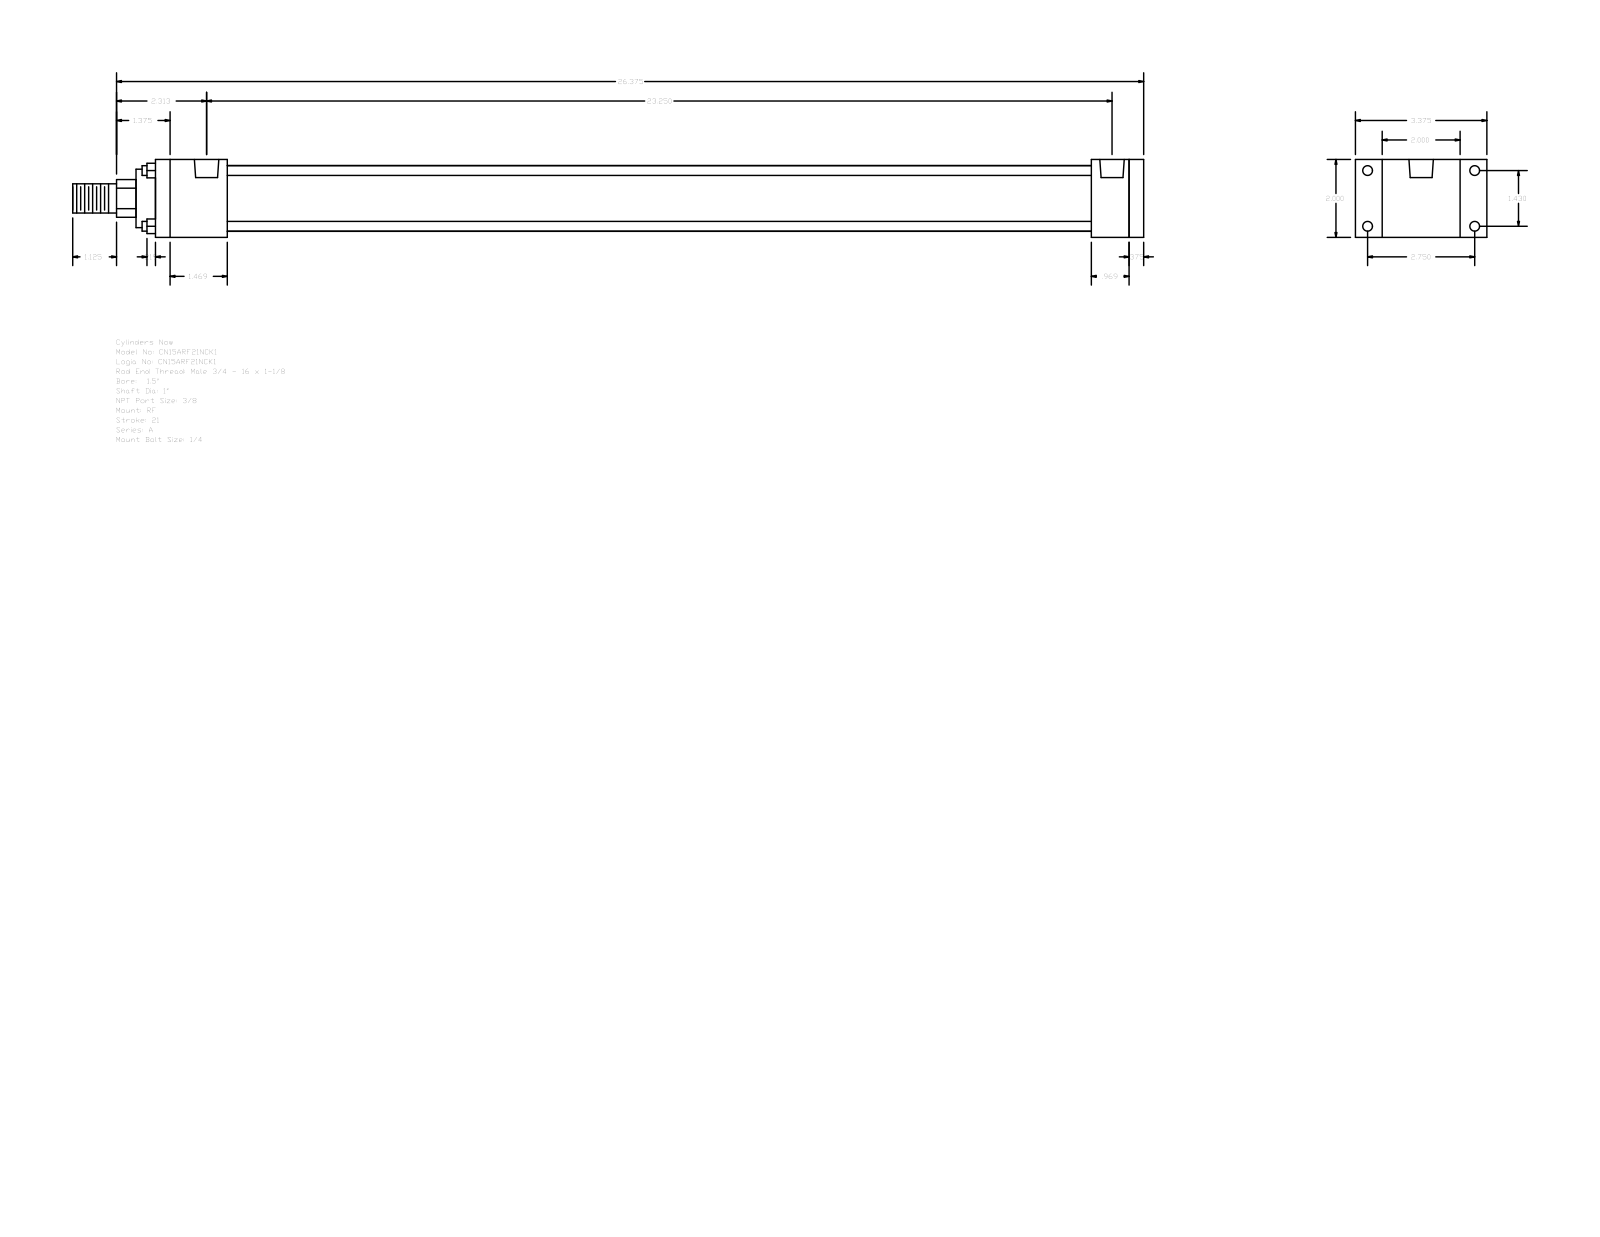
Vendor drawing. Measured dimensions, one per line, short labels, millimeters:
name: A_RF__0150_1
written by: GSSL Pune (CONFIG_CONTROL_DESIGN)
unit: mm
bodies: 0 solids, 92 faces (64 planar, 28 cylindrical, 0 other)
size: 698.5 × 85.72 × 50.8
holes: 4× ⌀5.56, 4× ⌀6.35, 2× ⌀15.93
bosses: 4× ⌀6.35, 1× ⌀42.93, 1× ⌀38.1, 1× ⌀25.4, 1× ⌀19.05
rounds: 1× R12.29
face distances: 50.8, 9.52, 635, 644.52, 610.39, 24.61, 34.13, 46.83, 563.56, 588.17
hole spacings: 3.97, 36.32, 69.84, 78.72, 582.61, 586.58, 590.55
